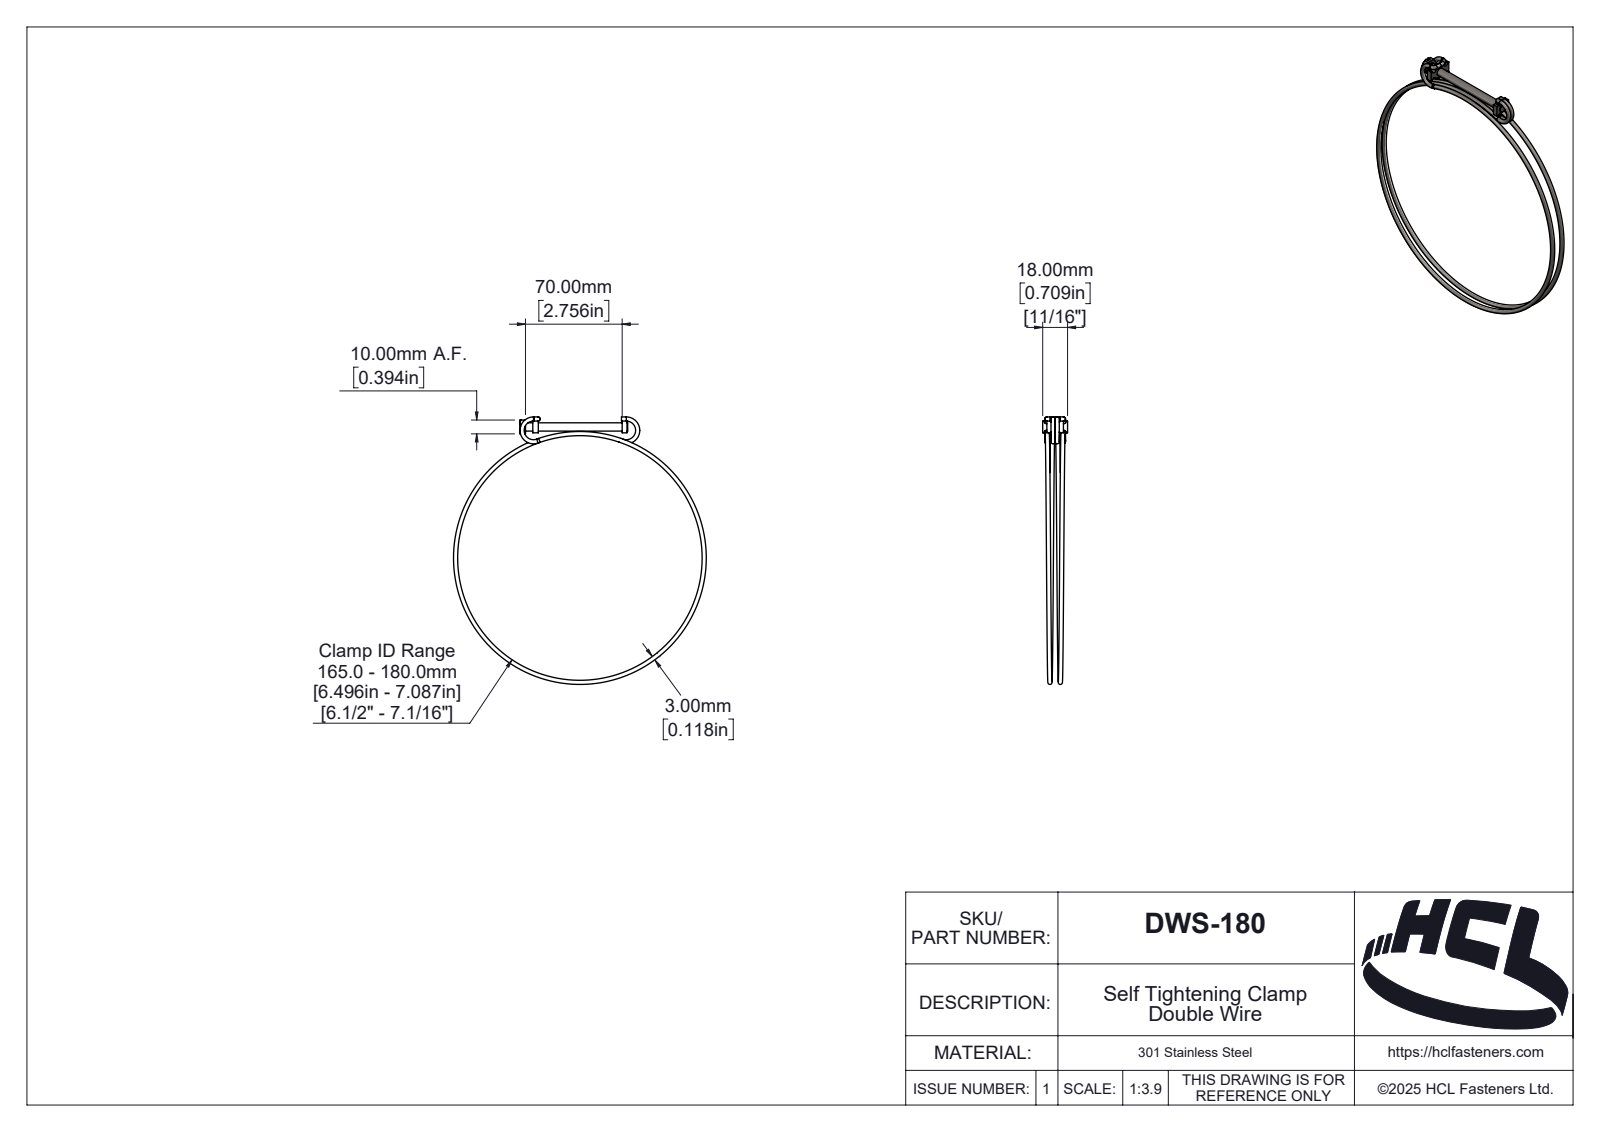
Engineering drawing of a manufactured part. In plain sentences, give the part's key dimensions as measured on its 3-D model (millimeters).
The part is named "DWS-180". Its 3-D file was written by "SolidWorks 2025 (AUTOMOTIVE_DESIGN)". It is 6 solids with 217 faces: 55 planar, 74 cylindrical and 88 other. Overall it measures 193.55 by 183 by 18 millimeters. Its volume is 12 862 cubic millimeters and its surface area 15 775 square millimeters. Round holes: 1 of diameter 6. Round bosses or shafts: 4 of diameter 3. Partial cylindrical surfaces (rounded edges, fillets, slot ends): 12 of radius 0.2, 4 of radius 1, 4 of radius 2, 1 of radius 0.4, 1 of radius 0.51, 1 of radius 0.53, 1 of radius 0.64, 1 of radius 0.91. The main face-to-face distances are 4, 9.3, 10, 64.7, 3, 74, 64.2, 73.5, 1, 68.2.
